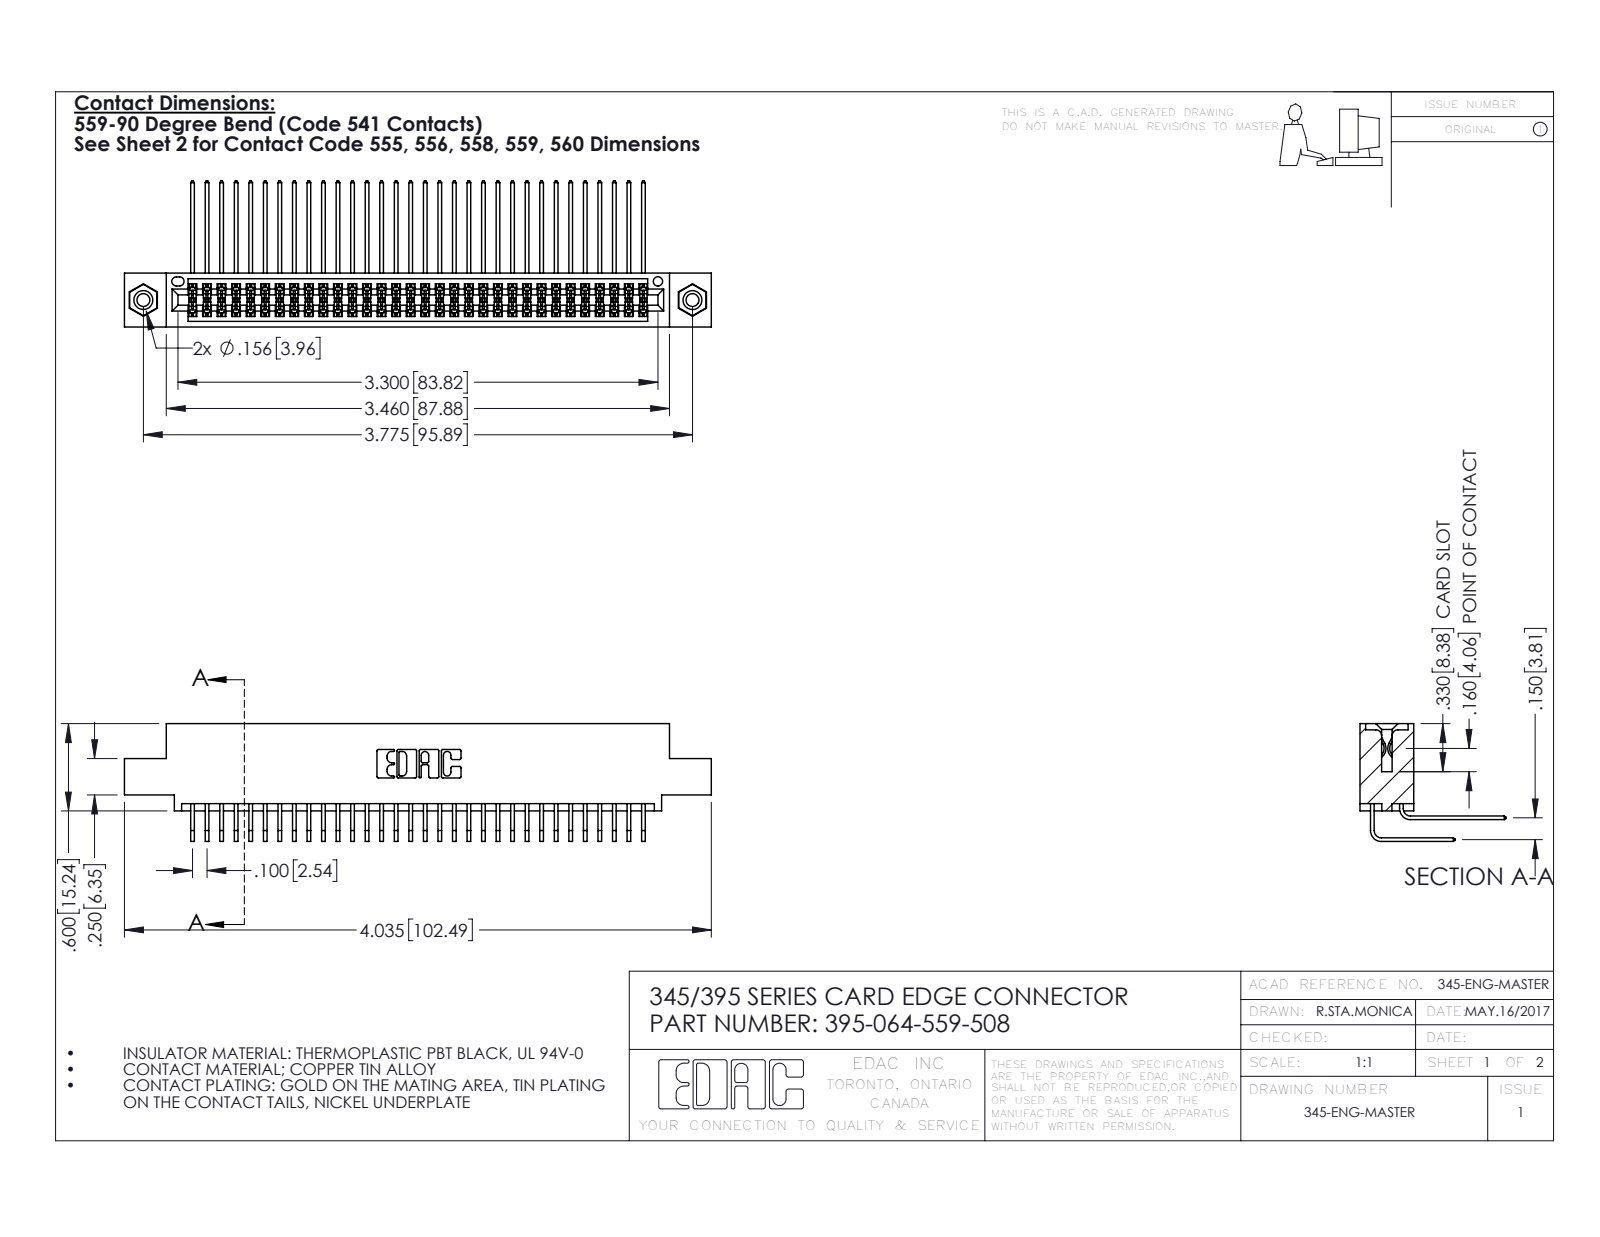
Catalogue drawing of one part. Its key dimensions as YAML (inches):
part_name: "345-292-001_558 559 Tail - 1; 345-292-001_559 Tail - 2; 345-250-001_345-250-003-102; 345 Part_0.110 Offset - 0.156 Dia-TI (+1 more)"
step_written_by: "SolidWorks 2016 (CONFIG_CONTROL_DESIGN)"
units: inches
bodies: {solids: 67, faces: 3518, planar: 2356, cylindrical: 1146, other: 16}
overall_size: [4.035, 1.005, 0.809]
volume: 0.62
surface_area: 25.82
round_holes:
  - {diameter: 0.089, count: 2}
  - {diameter: 0.125, count: 2}
  - {diameter: 0.156, count: 2}
  - {diameter: 0.064, count: 1}
round_bosses_or_shafts:
  - {diameter: 0.155, count: 2}
partial_cylinders:
  - {radius: 0.006, count: 96}
  - {radius: 0.01, count: 22}
  - {radius: 0.007, count: 6}
  - {radius: 0.031, count: 6}
  - {radius: 0.026, count: 3}
  - {radius: 0.014, count: 2}
  - {radius: 0.019, count: 2}
  - {radius: 0.022, count: 2}
face_to_face_distances: [0.072, 0.298, 0.2, 0.37, 0.098, 0.272, 0.025, 0.225, 0.175, 0.15]
hole_center_spacings: [0.27, 3.54, 3.775]
